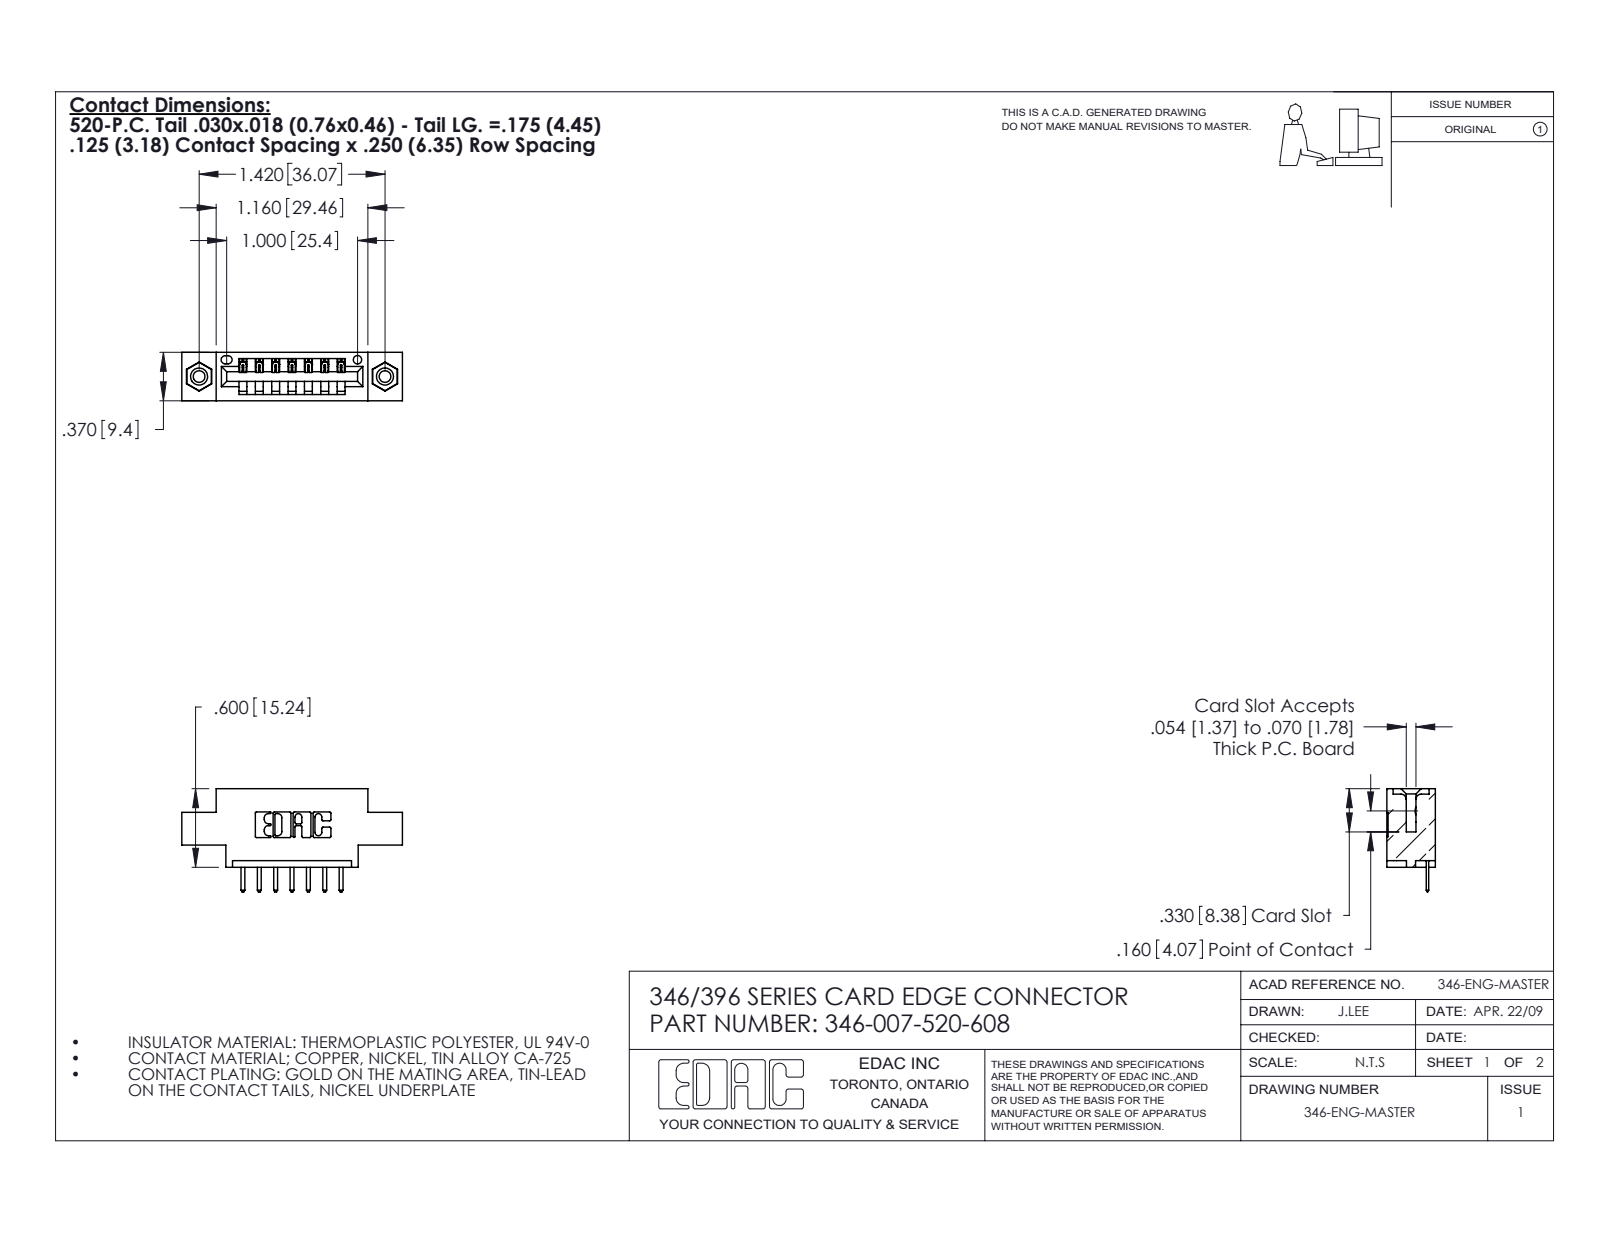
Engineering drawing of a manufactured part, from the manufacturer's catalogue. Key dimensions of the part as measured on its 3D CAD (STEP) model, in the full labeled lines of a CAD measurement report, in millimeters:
Part name (STEP PRODUCT): 346-007-520-608; 346 Part_0.170 Offset - 0.156 Dia-TI; 345-292-001_345-293-120; 345-250-001_345-250-003-102
STEP written by: SolidWorks 2020 (CONFIG_CONTROL_DESIGN)
Units: millimetres
Bodies: 10 solids, 620 faces (406 planar, 198 cylindrical, 16 other)
Overall size (bounding box): 42.8 × 20 × 9.4
Volume: 3 670 mm³ · Surface area: 4 330 mm²
Round holes (diameter × count): ⌀2.3 ×2, ⌀3.2 ×2, ⌀4 ×2, ⌀1.6 ×1
Round bosses / shafts (diameter × count): ⌀3.9 ×2
Partial cylindrical surfaces — rounded edges, fillets, slot ends (radius × count): R0.3 ×22, R0.3 ×16, R0.2 ×14, R0.2 ×6, R0.8 ×6, R0.7 ×3, R0.8 ×2, R1 ×2
Main face-to-face distances: 6.4, 9.4, 1.2, 8.2, 5.6, 3.8, 2.5, 4.4, 3.2, 4.7
Hole centre spacings: 6.2, 30.9, 36.1
